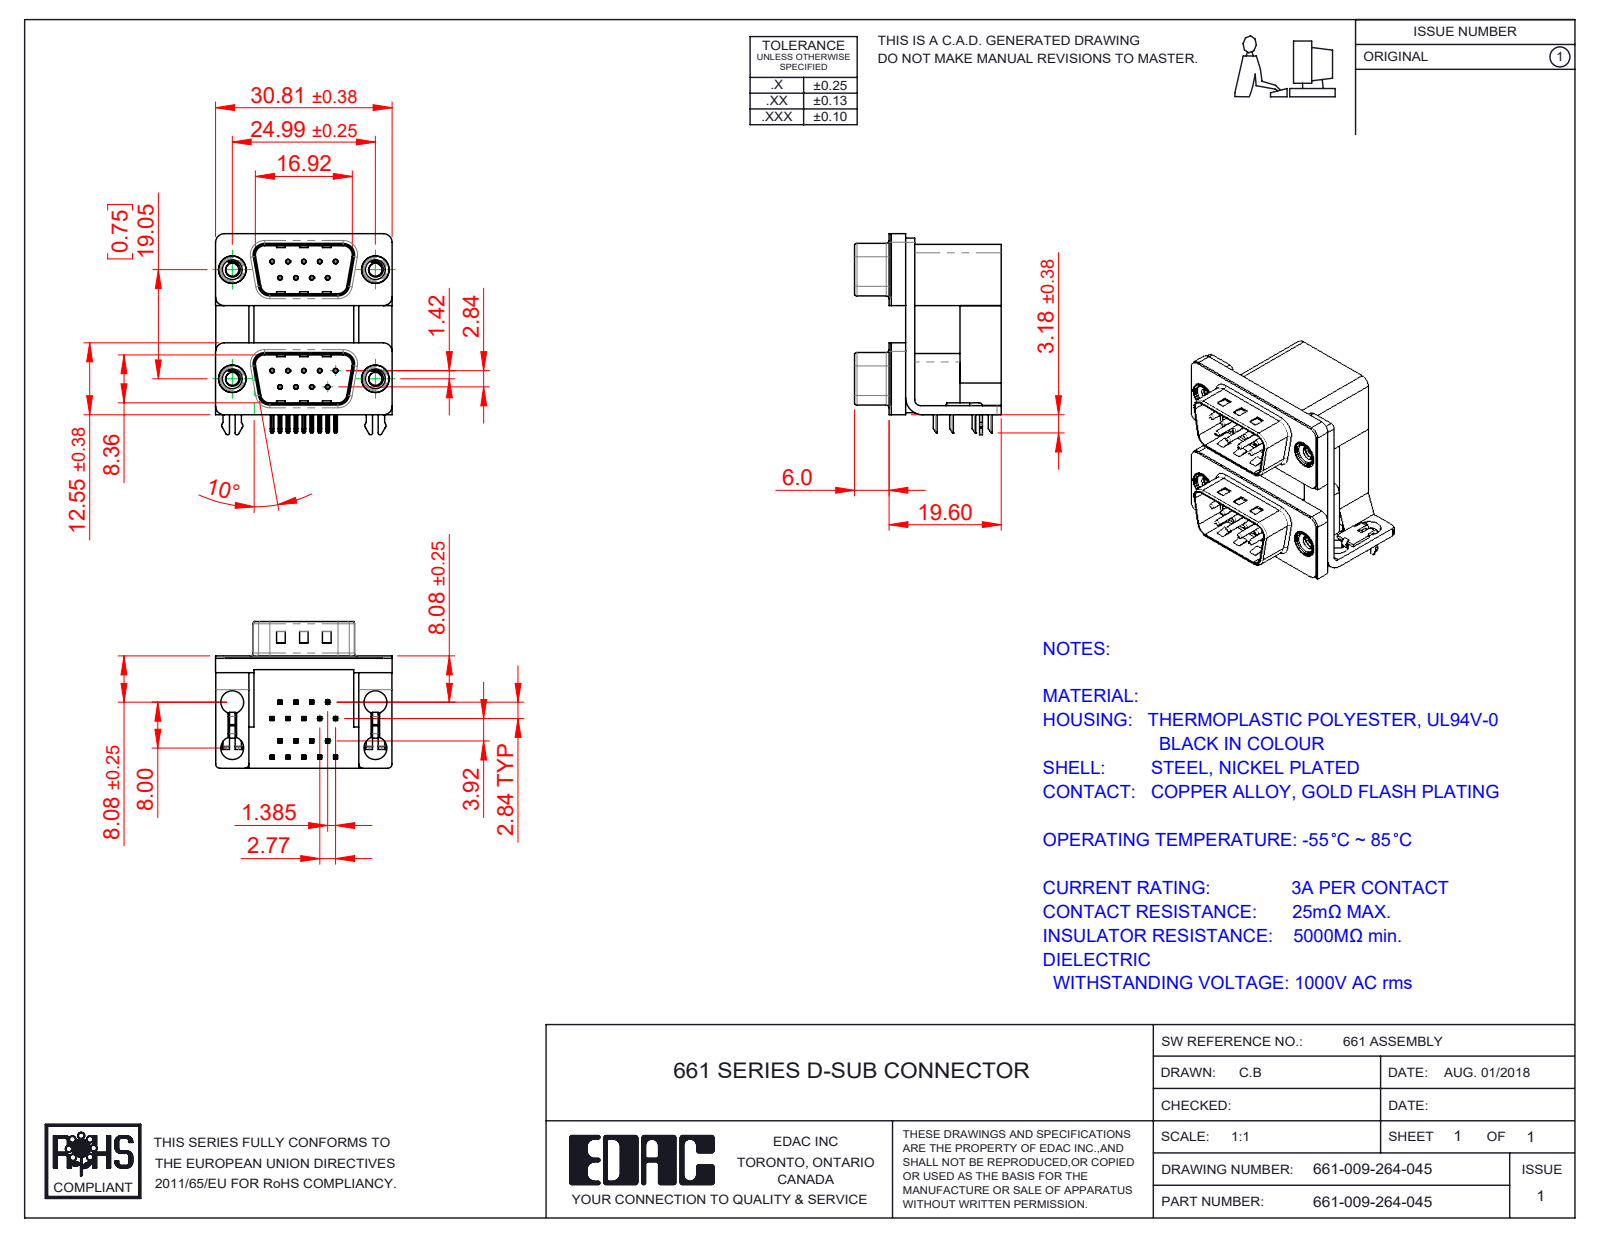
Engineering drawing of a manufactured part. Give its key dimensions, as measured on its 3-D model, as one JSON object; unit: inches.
{"part_name": "661-009-264-045; 661 Mounting Bracket_2ProngM; 661 Housing Spacer_09 Contacts M; 661 Shell_09 Contacts (+8 more)", "step_written_by": "SolidWorks 2020 (CONFIG_CONTROL_DESIGN)", "units": "inches", "bodies": {"solids": 31, "faces": 2056, "planar": 1230, "cylindrical": 624, "other": 202}, "overall_size": [1.382, 1.213, 1.008], "volume_in3": 0.627, "surface_area_in2": 18.57, "round_holes": [[0.014, 18], [0.031, 18], [0.157, 8], [0.089, 4], [0.138, 4], [0.189, 4], [0.197, 4]], "round_bosses_or_shafts": [[0.03, 18], [0.193, 4], [0.187, 4], [0.154, 4]], "partial_cylinders_radius": [[0.01, 78], [0.005, 36], [0.02, 20], [0.059, 14], [0.03, 10], [0.035, 8], [0.063, 8], [0.079, 8]], "face_to_face_distances": [0.016, 0.098, 0.75, 0.657, 0.756, 0.283, 0.421, 0.374, 0.472, 0.063], "hole_center_spacings": [0.124, 0.109, 0.758, 0.75, 0.218, 0.781, 0.641, 0.863]}
